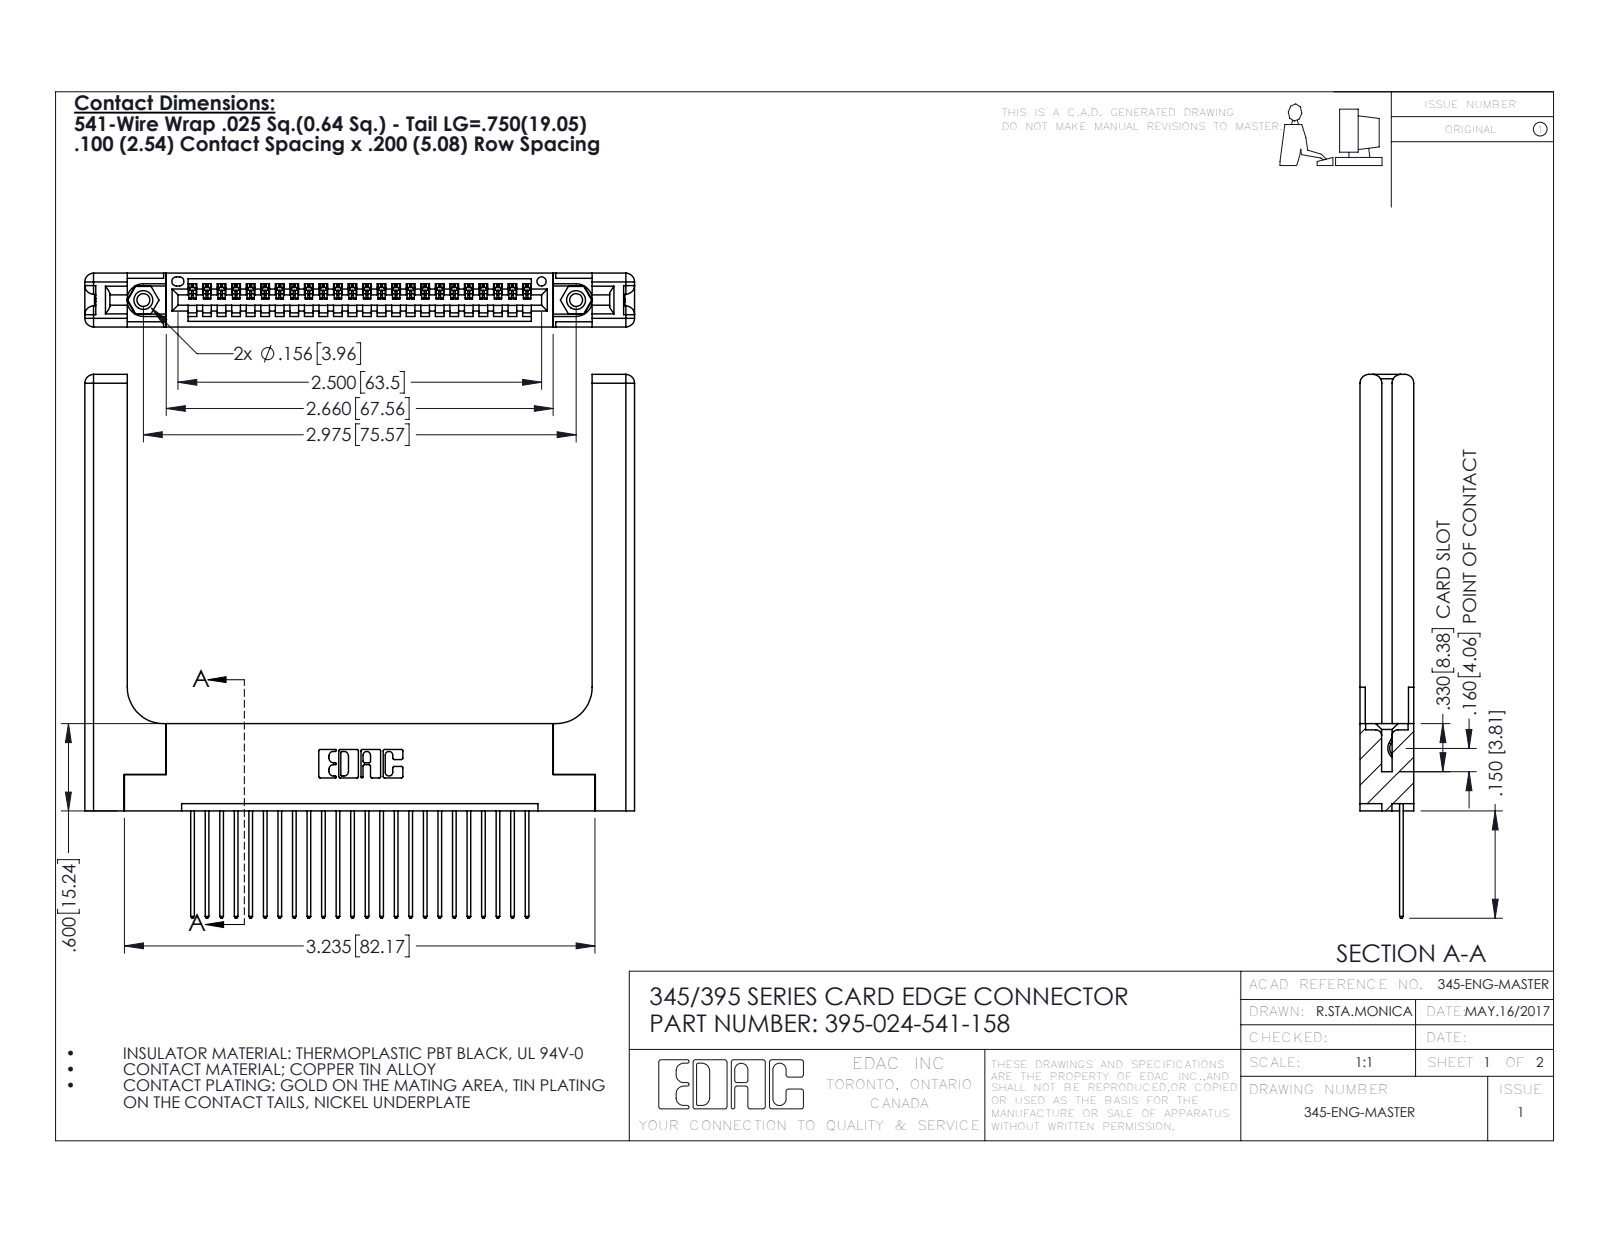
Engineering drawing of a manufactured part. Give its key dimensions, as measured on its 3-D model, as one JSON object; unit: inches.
{"part_name": "395-024-541-158; 345-250-001_345-250-001-102; 345 Part_Flush Mounting Lugs - 0.156 Dia-TH; 345-292-001_345-293-141 (+1 more)", "step_written_by": "SolidWorks 2016 (CONFIG_CONTROL_DESIGN)", "units": "inches", "bodies": {"solids": 29, "faces": 1774, "planar": 1188, "cylindrical": 526, "other": 60}, "overall_size": [3.779, 3.737, 0.37], "volume_in3": 1.071, "surface_area_in2": 27.21, "round_holes": [[0.089, 2], [0.125, 2], [0.156, 2], [0.064, 1]], "round_bosses_or_shafts": [[0.155, 2]], "partial_cylinders_radius": [[0.006, 48], [0.01, 48], [0.01, 22], [0.06, 16], [0.007, 6], [0.031, 6], [0.026, 3], [0.03, 2]], "face_to_face_distances": [0.37, 0.072, 0.298, 0.2, 0.098, 0.272, 0.025, 0.148, 0.15, 0.077], "hole_center_spacings": [0.27, 2.741, 2.975]}
